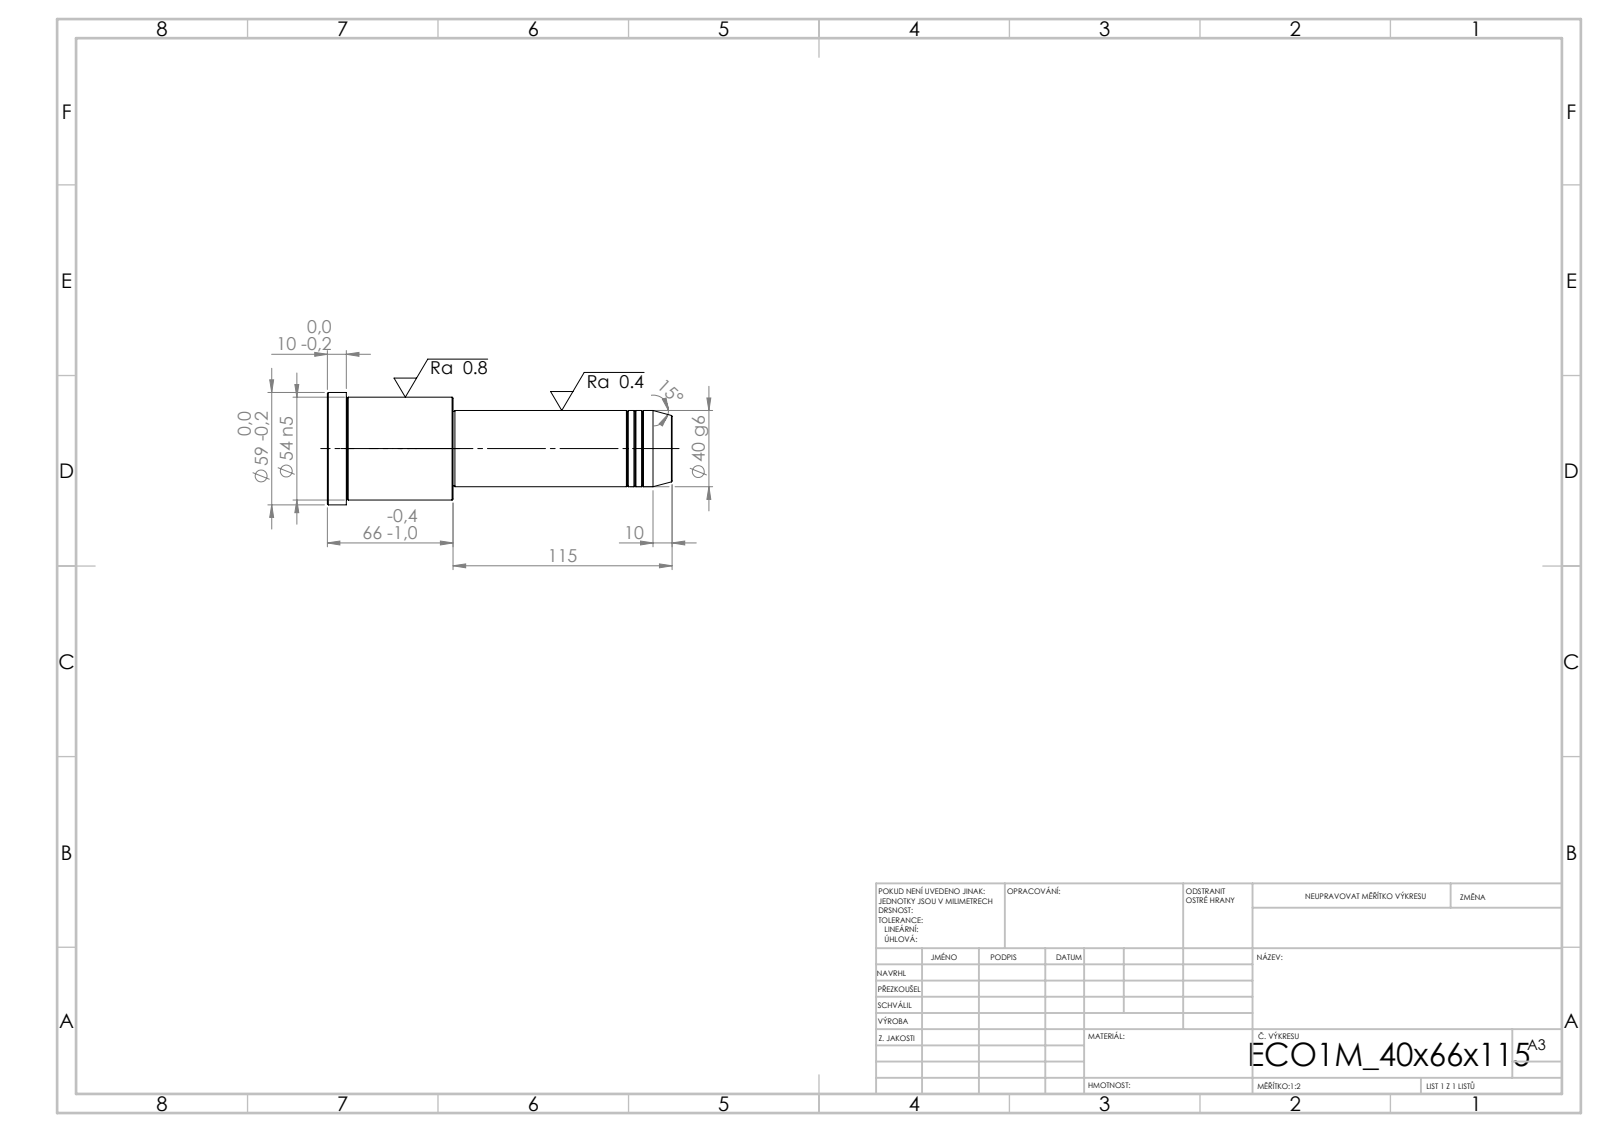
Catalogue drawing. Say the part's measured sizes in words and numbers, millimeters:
Its 3-D file was written by "SolidWorks 2019 (CONFIG_CONTROL_DESIGN)". It is 1 solid with 43 faces: 5 planar, 14 cylindrical and 24 other. Overall it measures 181 by 59 by 59 millimeters. Its volume is 298 175 cubic millimeters and its surface area 31 219 square millimeters. Round bosses or shafts: 1 of diameter 59, 1 of diameter 54, 1 of diameter 40, 1 of diameter 39. The main face-to-face distances are 66, 115, 181, 171, 56, 10, 114, 1, 57, 67.
